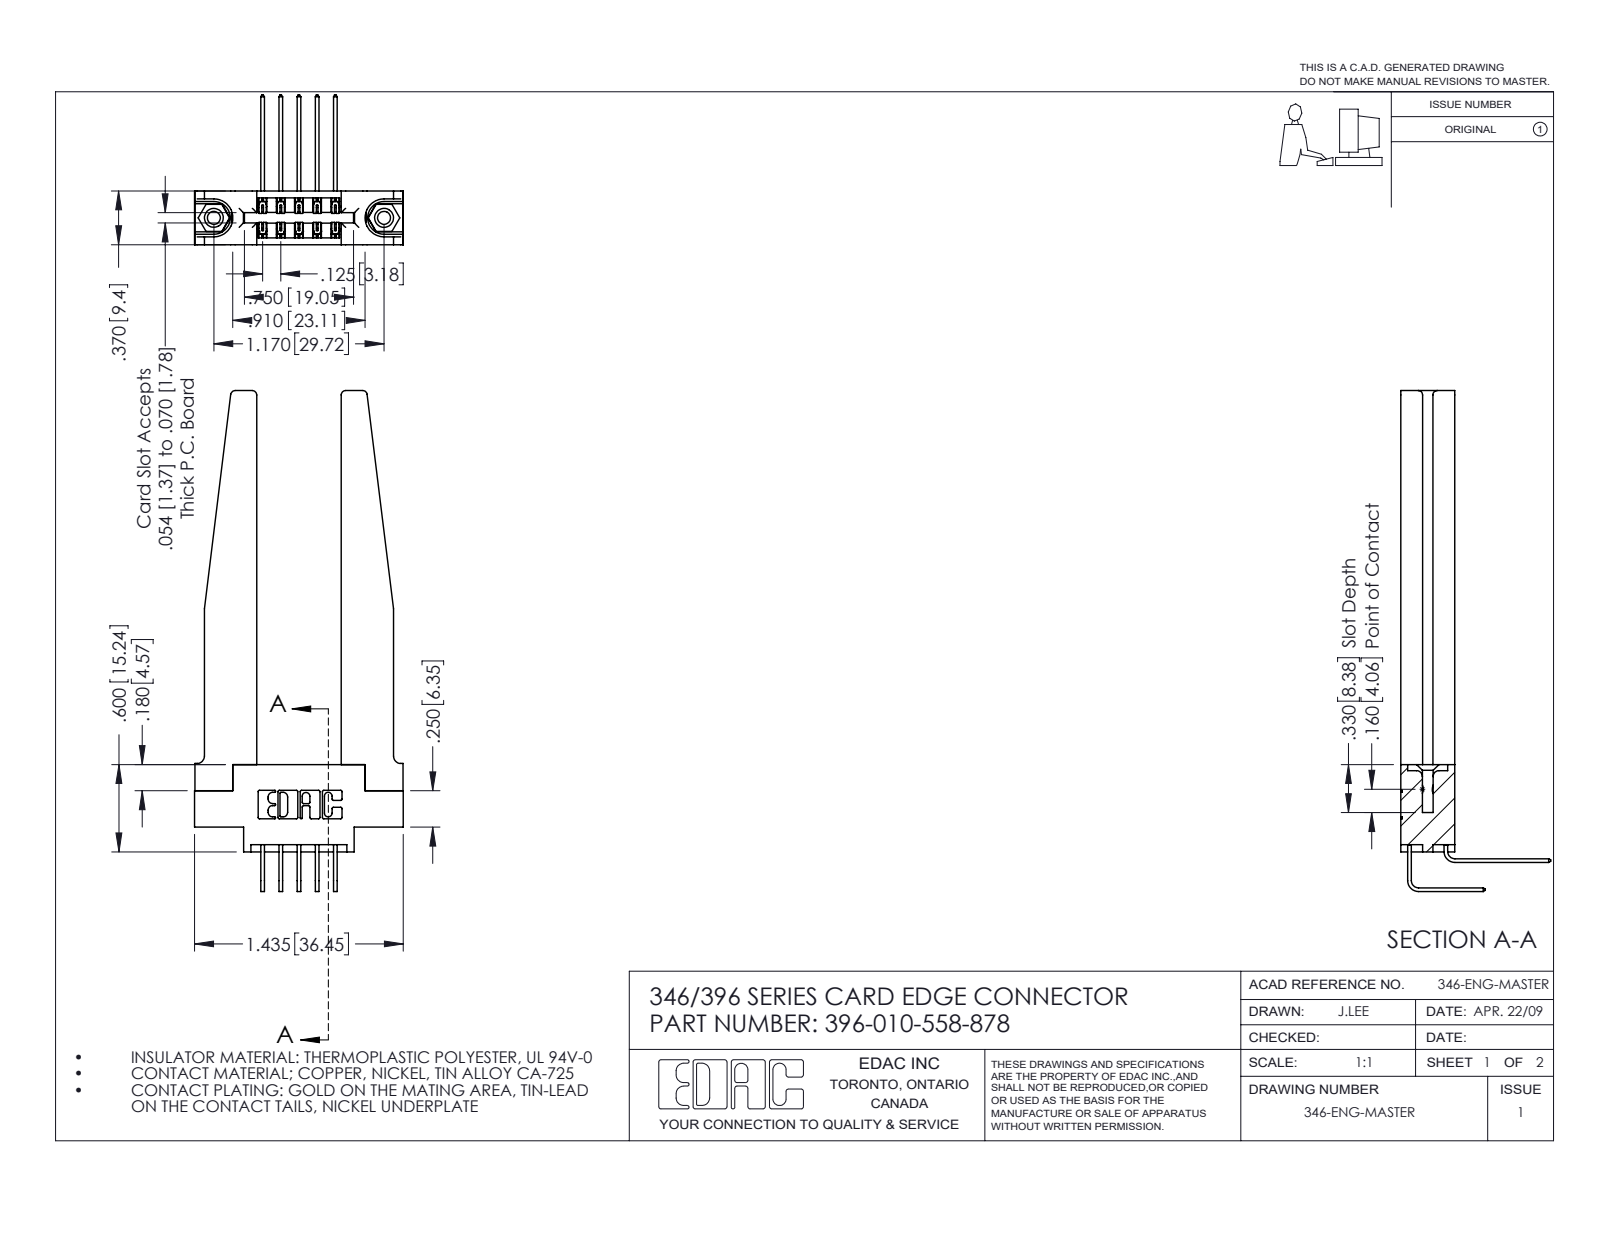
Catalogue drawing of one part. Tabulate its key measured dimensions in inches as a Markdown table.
| quantity | value |
| --- | --- |
| part name | 346 Part_0.170 Offset - 0.156 Dia-TH; 345-292-001_558 Tail - 2; 396-010-558-878; 345-292-001_558 559 Tail - 1 (+2 more) |
| STEP written by | SolidWorks 2016 (CONFIG_CONTROL_DESIGN) |
| units | inches |
| bodies | 15 solids, 900 faces (592 planar, 256 cylindrical, 52 other) |
| overall size | 3.443 × 1.435 × 1.03 |
| volume | 0.615 in³ |
| surface area | 16.69 in² |
| round holes (diameter × count) | 0.089 × 2, 0.125 × 2, 0.156 × 2, 0.064 × 1 |
| round bosses / shafts (diameter × count) | 0.155 × 2 |
| partial cylindrical surfaces (radius × count) | 0.01 × 22, 0.006 × 15, 0.03 × 8, 0.007 × 6, 0.031 × 6, 0.05 × 4, 0.026 × 3, 0.014 × 2 |
| main face-to-face distances | 0.37, 0.15, 0.22, 0.581, 0.25, 0.072, 0.048, 0.148, 0.322, 0.102 |
| hole center spacings | 0.246, 0.969, 1.17 |
